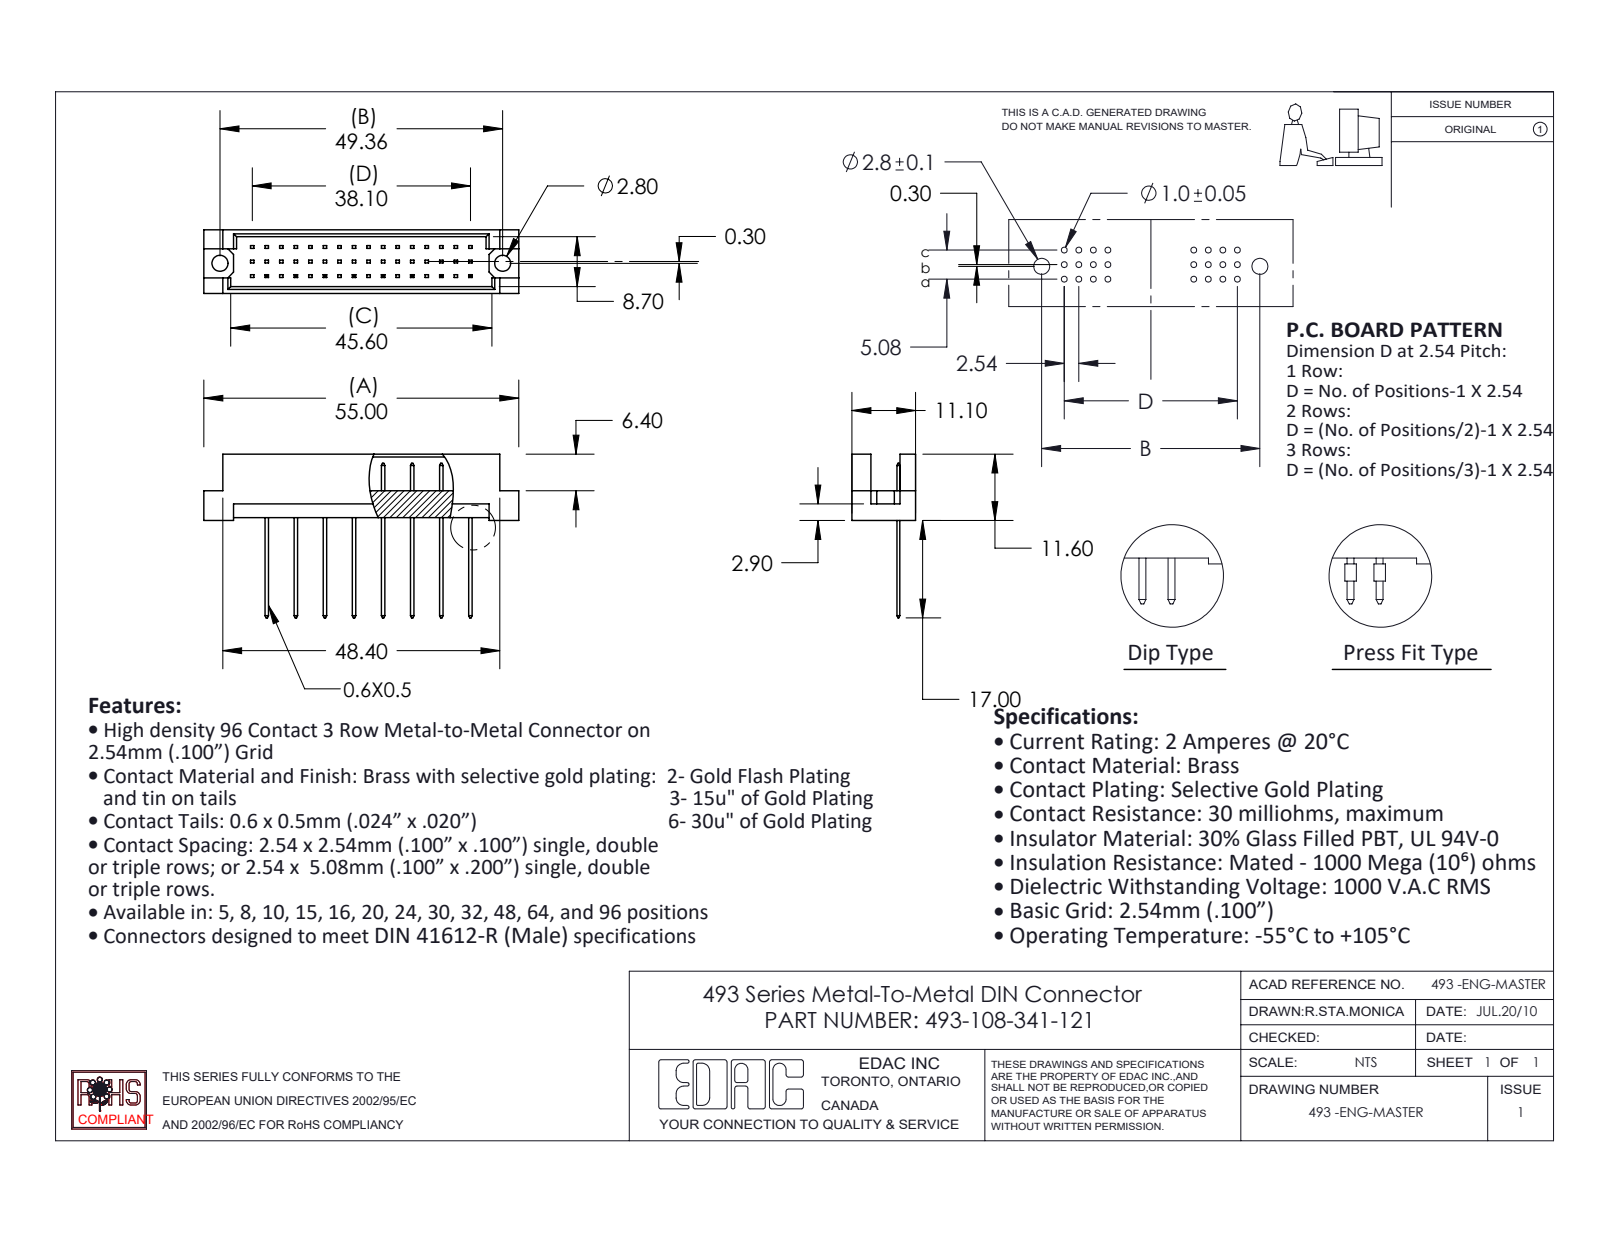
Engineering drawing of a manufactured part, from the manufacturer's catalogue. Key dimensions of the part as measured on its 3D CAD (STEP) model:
Part name (STEP PRODUCT): 493-108-341-121; 493-290_41; 493 Part_48
STEP written by: SolidWorks 2020 (CONFIG_CONTROL_DESIGN)
Units: millimetres
Bodies: 9 solids, 356 faces (352 planar, 4 cylindrical, 0 other)
Overall size (bounding box): 55 × 28.6 × 11.1
Volume: 3 336 mm³ · Surface area: 4 229 mm²
Round holes (diameter × count): ⌀2.8 ×2
Main face-to-face distances: 1.2, 9.9, 11.1, 8.7, 5.08, 4.7, 0.5, 10.16, 2.76, 8.34
Hole centre spacings: 49.36
